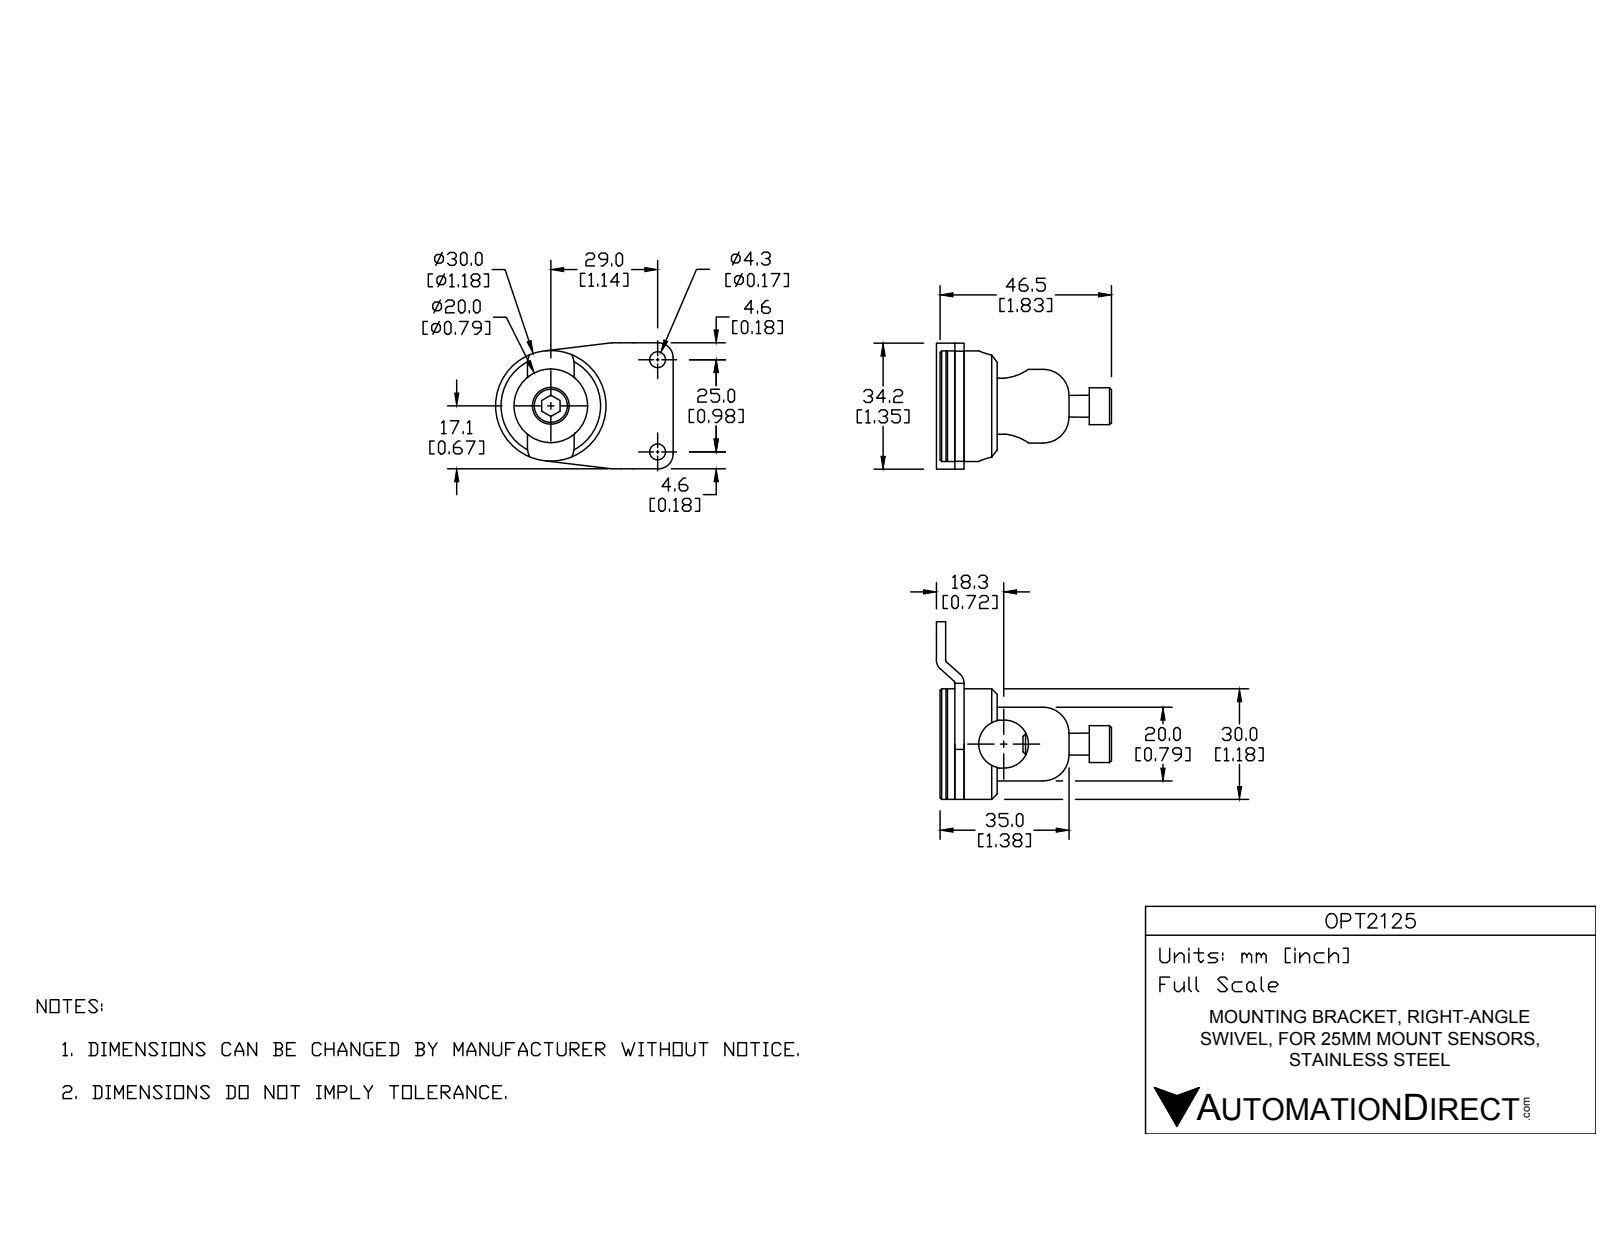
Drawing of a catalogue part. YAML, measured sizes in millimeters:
step_written_by: "Unknown (CONFIG_CONTROL_DESIGN)"
units: millimeters
bodies: {solids: 4, faces: 126, planar: 62, cylindrical: 46, other: 18}
overall_size: [63.6, 48.6, 34.2]
volume: 31094
surface_area: 17532
round_holes:
  - {diameter: 4.3, count: 4}
  - {diameter: 20.1, count: 2}
  - {diameter: 20, count: 1}
  - {diameter: 21, count: 1}
round_bosses_or_shafts:
  - {diameter: 30, count: 1}
  - {diameter: 10, count: 1}
partial_cylinders:
  - {radius: 1, count: 4}
  - {radius: 3.5, count: 4}
  - {radius: 4, count: 4}
  - {radius: 6.5, count: 3}
  - {radius: 15, count: 1}
face_to_face_distances: [2.5, 4.5, 4, 6.5, 2, 7, 9, 16, 11.5, 15.5]
hole_center_spacings: [31.95, 25]
